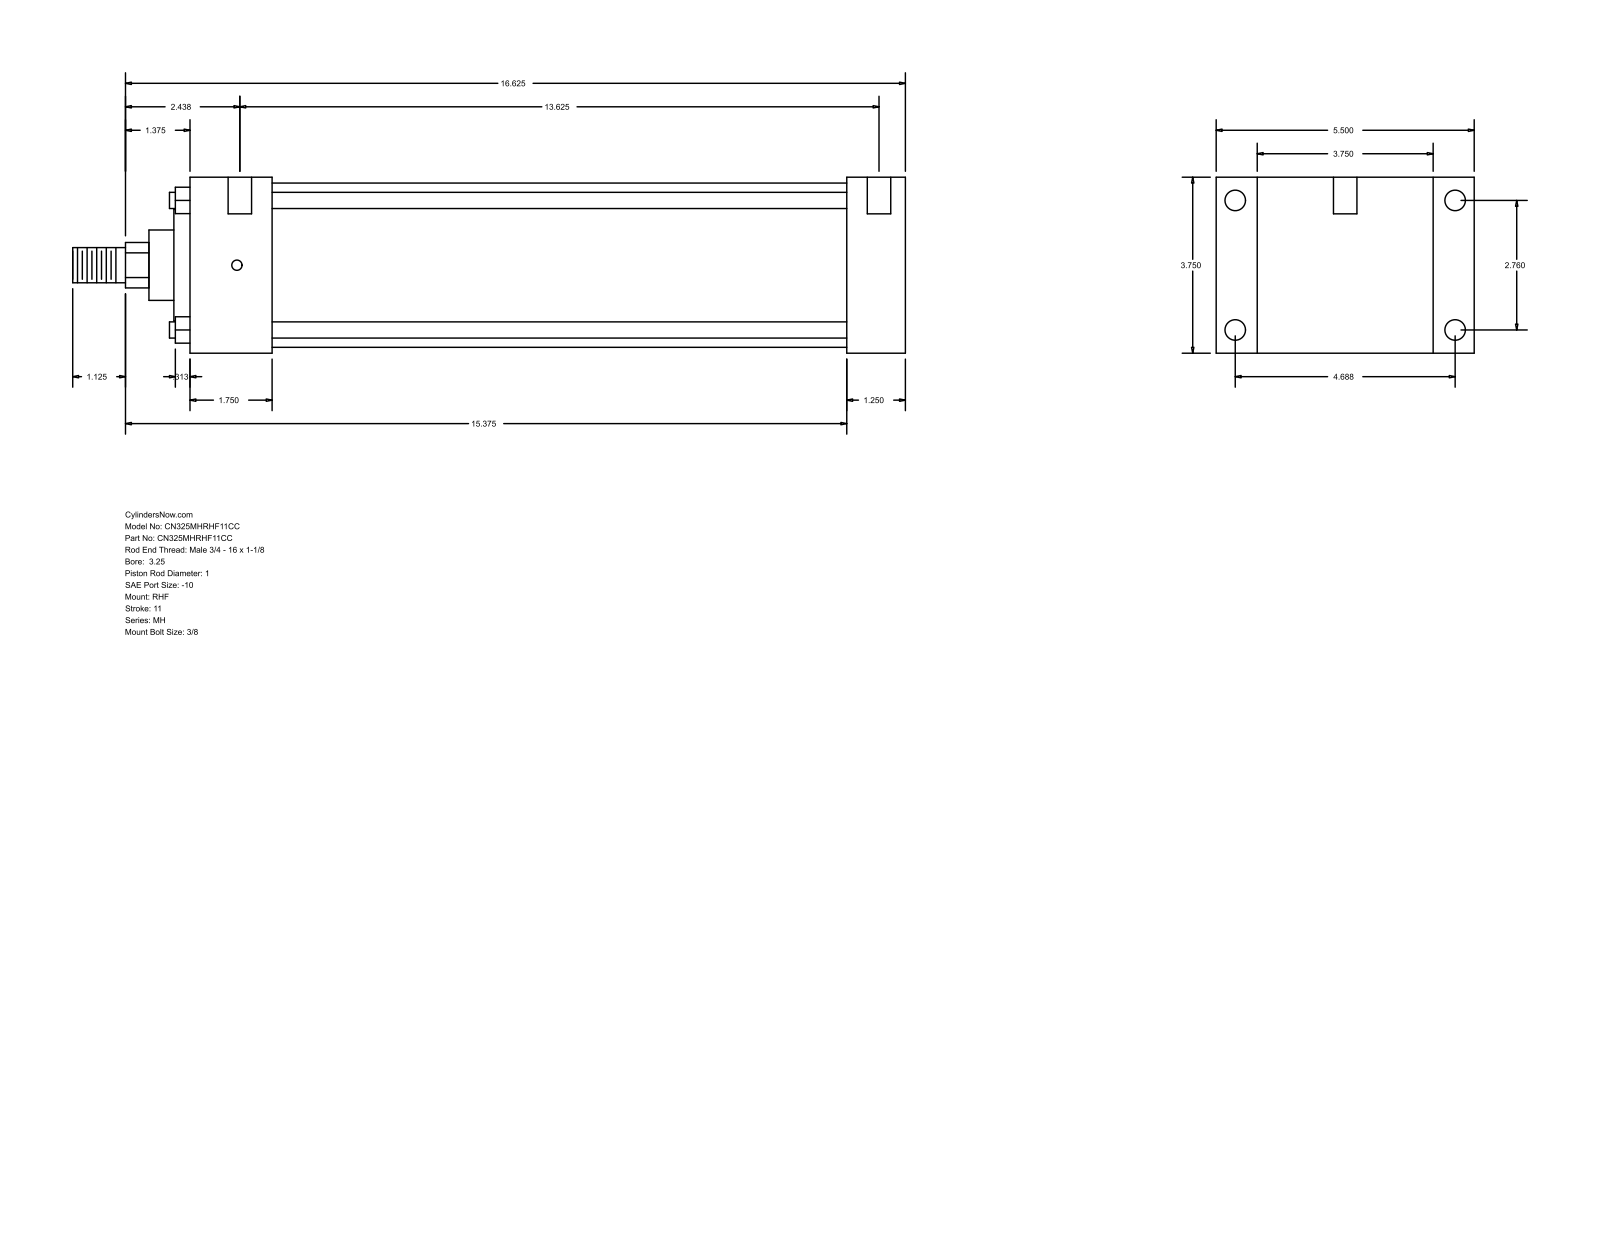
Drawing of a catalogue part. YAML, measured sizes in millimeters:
part_name: "MH_RHF__0325_1"
step_written_by: "GSSL Pune (CONFIG_CONTROL_DESIGN)"
units: millimeters
bodies: {solids: 0, faces: 90, planar: 61, cylindrical: 29, other: 0}
overall_size: [450.85, 139.7, 95.25]
round_holes:
  - {diameter: 5.56, count: 4}
  - {diameter: 11.13, count: 4}
  - {diameter: 12.7, count: 2}
round_bosses_or_shafts:
  - {diameter: 8.76, count: 4}
  - {diameter: 88.9, count: 1}
  - {diameter: 60.33, count: 1}
  - {diameter: 38.1, count: 1}
  - {diameter: 25.4, count: 1}
  - {diameter: 19.05, count: 1}
partial_cylinders:
  - {radius: 12.29, count: 1}
face_to_face_distances: [95.24, 31.75, 22.23, 117.47, 355.6, 387.35, 139.7, 44.46, 311.14, 342.89]
hole_center_spacings: [70.1, 119.06, 138.16, 352.42, 1.58, 4.76, 346.08, 347.66]
